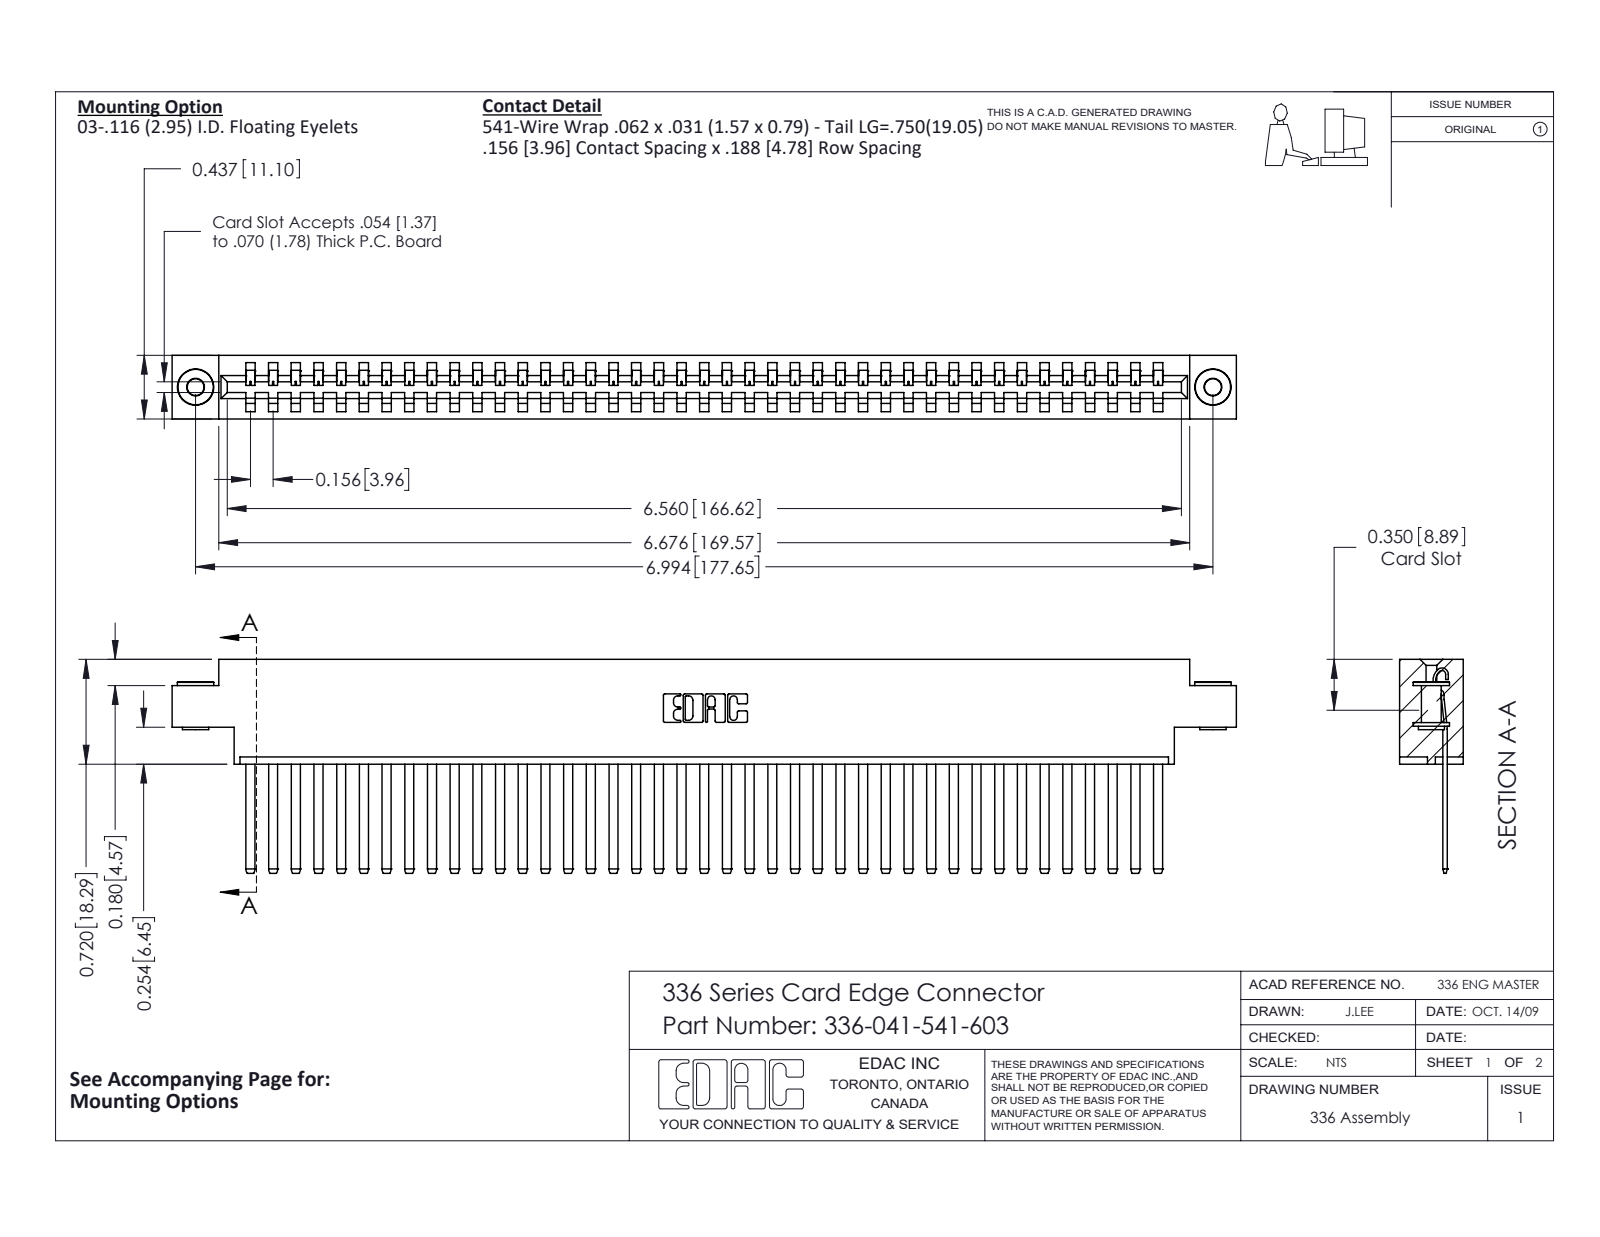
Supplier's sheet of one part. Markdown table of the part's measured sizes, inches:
| quantity | value |
| --- | --- |
| part name | 336 Part_Offset - .156 Dia - TH; 345-250-002_345-250-002-102; 336-041-541-603; 336-290-001_336-290-541 |
| STEP written by | SolidWorks 2020 (CONFIG_CONTROL_DESIGN) |
| units | inches |
| bodies | 44 solids, 2206 faces (1478 planar, 720 cylindrical, 8 other) |
| overall size | 7.317 × 1.47 × 0.437 |
| volume | 1.652 in³ |
| surface area | 46.13 in² |
| round holes (diameter × count) | 0.116 × 2, 0.156 × 2 |
| round bosses / shafts (diameter × count) | 0.25 × 2, 0.18 × 2, 0.136 × 2 |
| partial cylindrical surfaces (radius × count) | 0.004 × 82, 0.056 × 82, 0.01 × 22, 0.007 × 6, 0.031 × 6, 0.026 × 3, 0.022 × 2, 0.04 × 2 |
| main face-to-face distances | 0.437, 0.031, 0.181, 0.328, 0.14, 0.297, 0.109, 0.256, 0.05, 0.387 |
| hole center spacings | 6.994 |
